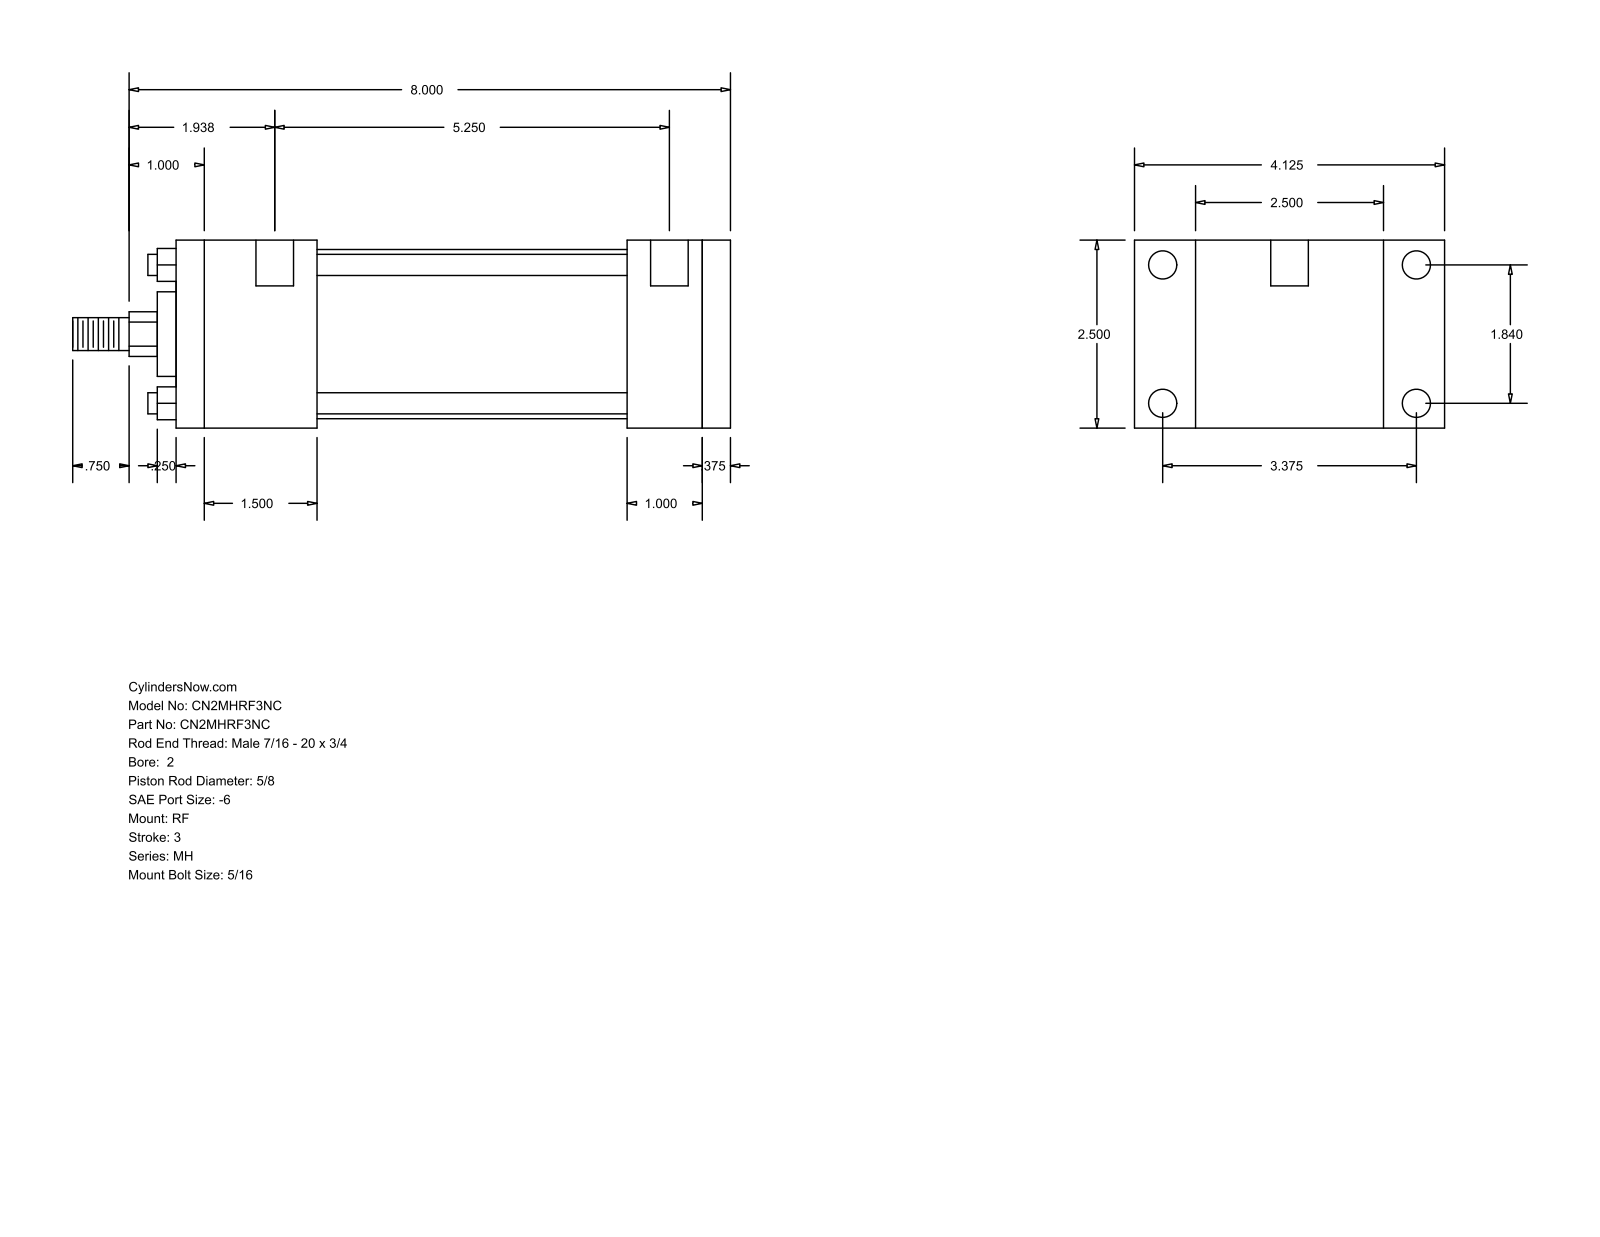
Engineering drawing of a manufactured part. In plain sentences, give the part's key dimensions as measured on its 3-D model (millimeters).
The part is named "MH_RF__0200_0.625". Its 3-D file was written by "GSSL Pune (CONFIG_CONTROL_DESIGN)". It is 0 solids with 92 faces: 64 planar, 28 cylindrical and 0 other. Overall it measures 222.25 by 104.78 by 63.5 millimeters. Round holes: 4 of diameter 5.56, 4 of diameter 9.53, 2 of diameter 12.7. Round bosses or shafts: 4 of diameter 7.14, 1 of diameter 57.15, 1 of diameter 28.57, 1 of diameter 15.88, 1 of diameter 11.11. Partial cylindrical surfaces (rounded edges, fillets, slot ends): 1 of radius 7.54. The main face-to-face distances are 63.5, 187.32, 177.8, 9.52, 104.78, 25.4, 47.62, 152.4, 130.18, 139.7. The hole center spacings are 46.74, 85.72, 97.63, 141.29, 3.18, 4.76, 133.35, 136.53.
